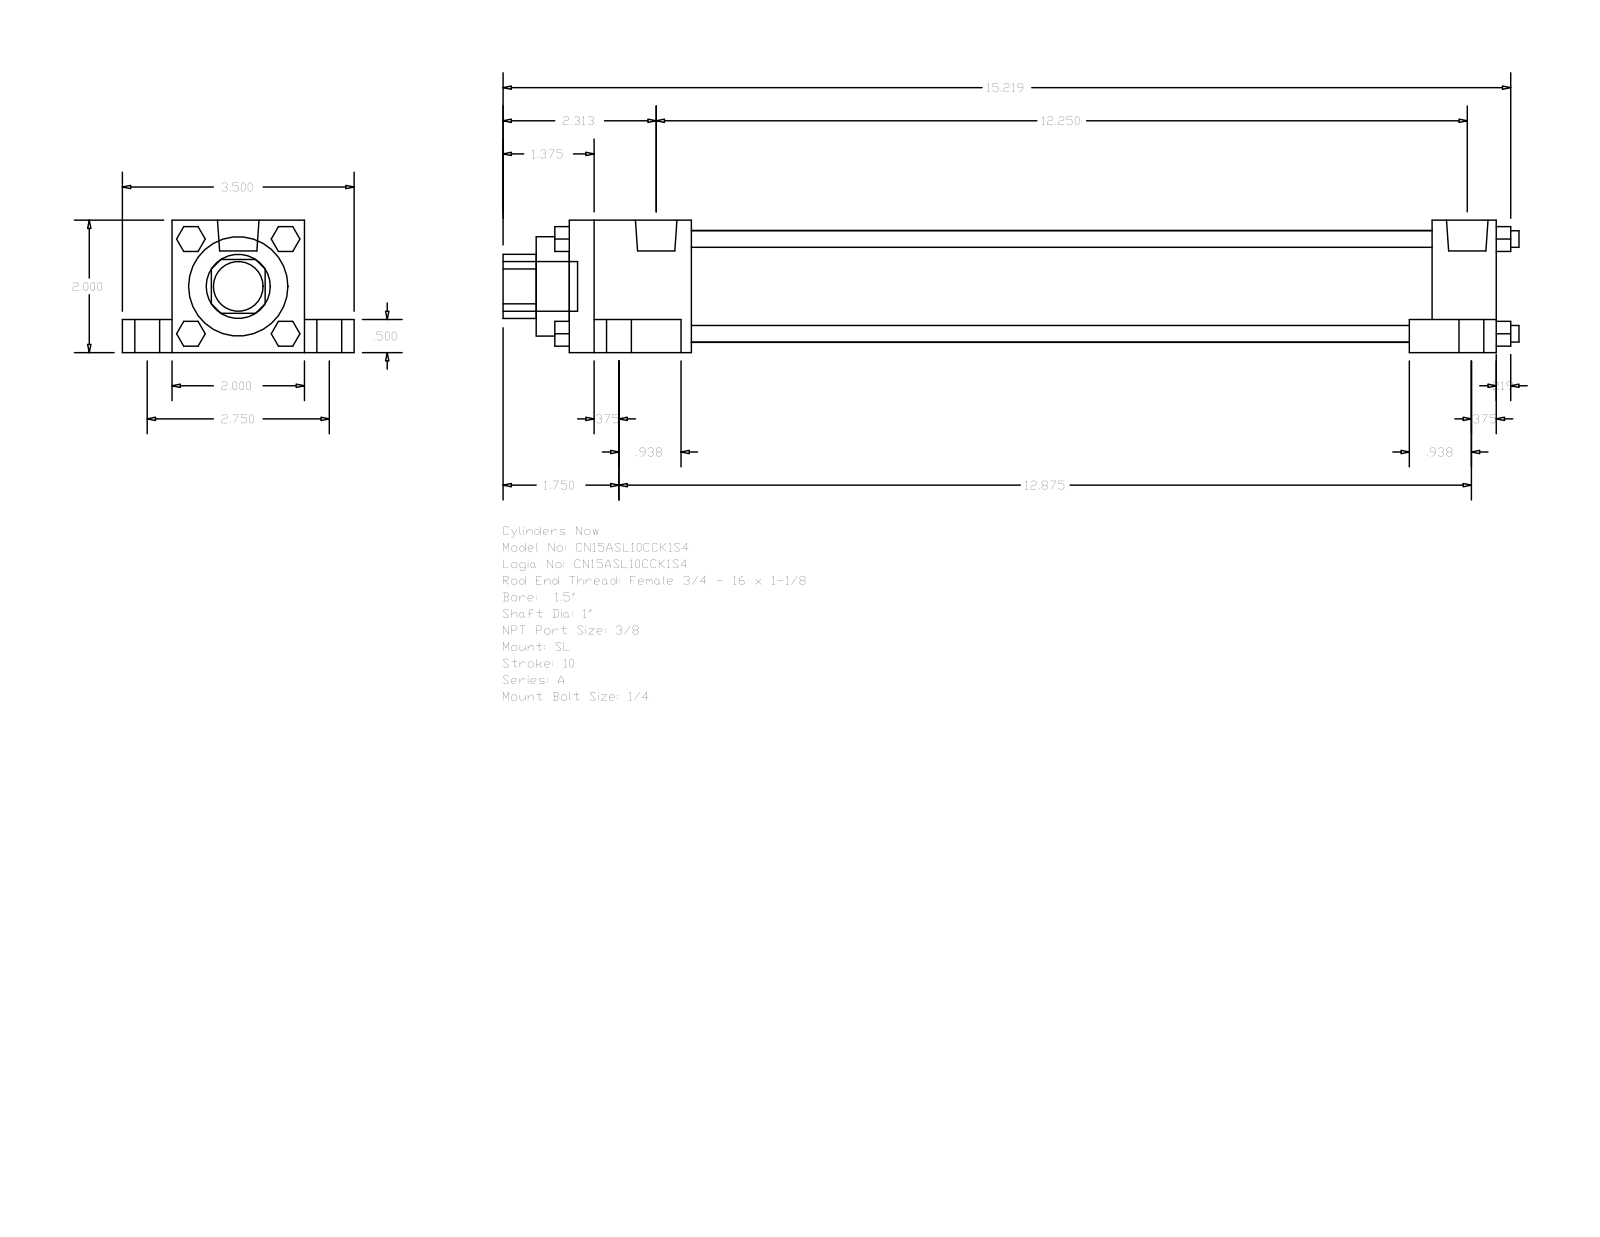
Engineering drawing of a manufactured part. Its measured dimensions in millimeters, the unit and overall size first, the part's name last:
Units: millimetres
Overall size (bounding box): 389.73 × 88.9 × 50.8
Round holes (diameter × count): ⌀25.4 ×1, ⌀38.1 ×1, ⌀42.93 ×1
Round bosses / shafts (diameter × count): ⌀15.88 ×4, ⌀9.53 ×4, ⌀6.35 ×4, ⌀5.56 ×4, ⌀15.93 ×2, ⌀19.05 ×1
Partial cylindrical surfaces — rounded edges, fillets, slot ends (radius × count): R12.29 ×1
Main face-to-face distances: 50.8, 12.7, 38.1, 19.05, 69.85, 9.52, 355.6, 33.34, 330.99, 24.61
Bodies: 0 solids, 148 faces (112 planar, 36 cylindrical, 0 other)
Part name (STEP PRODUCT): A_SL__0150_1
STEP written by: GSSL Pune (CONFIG_CONTROL_DESIGN)
